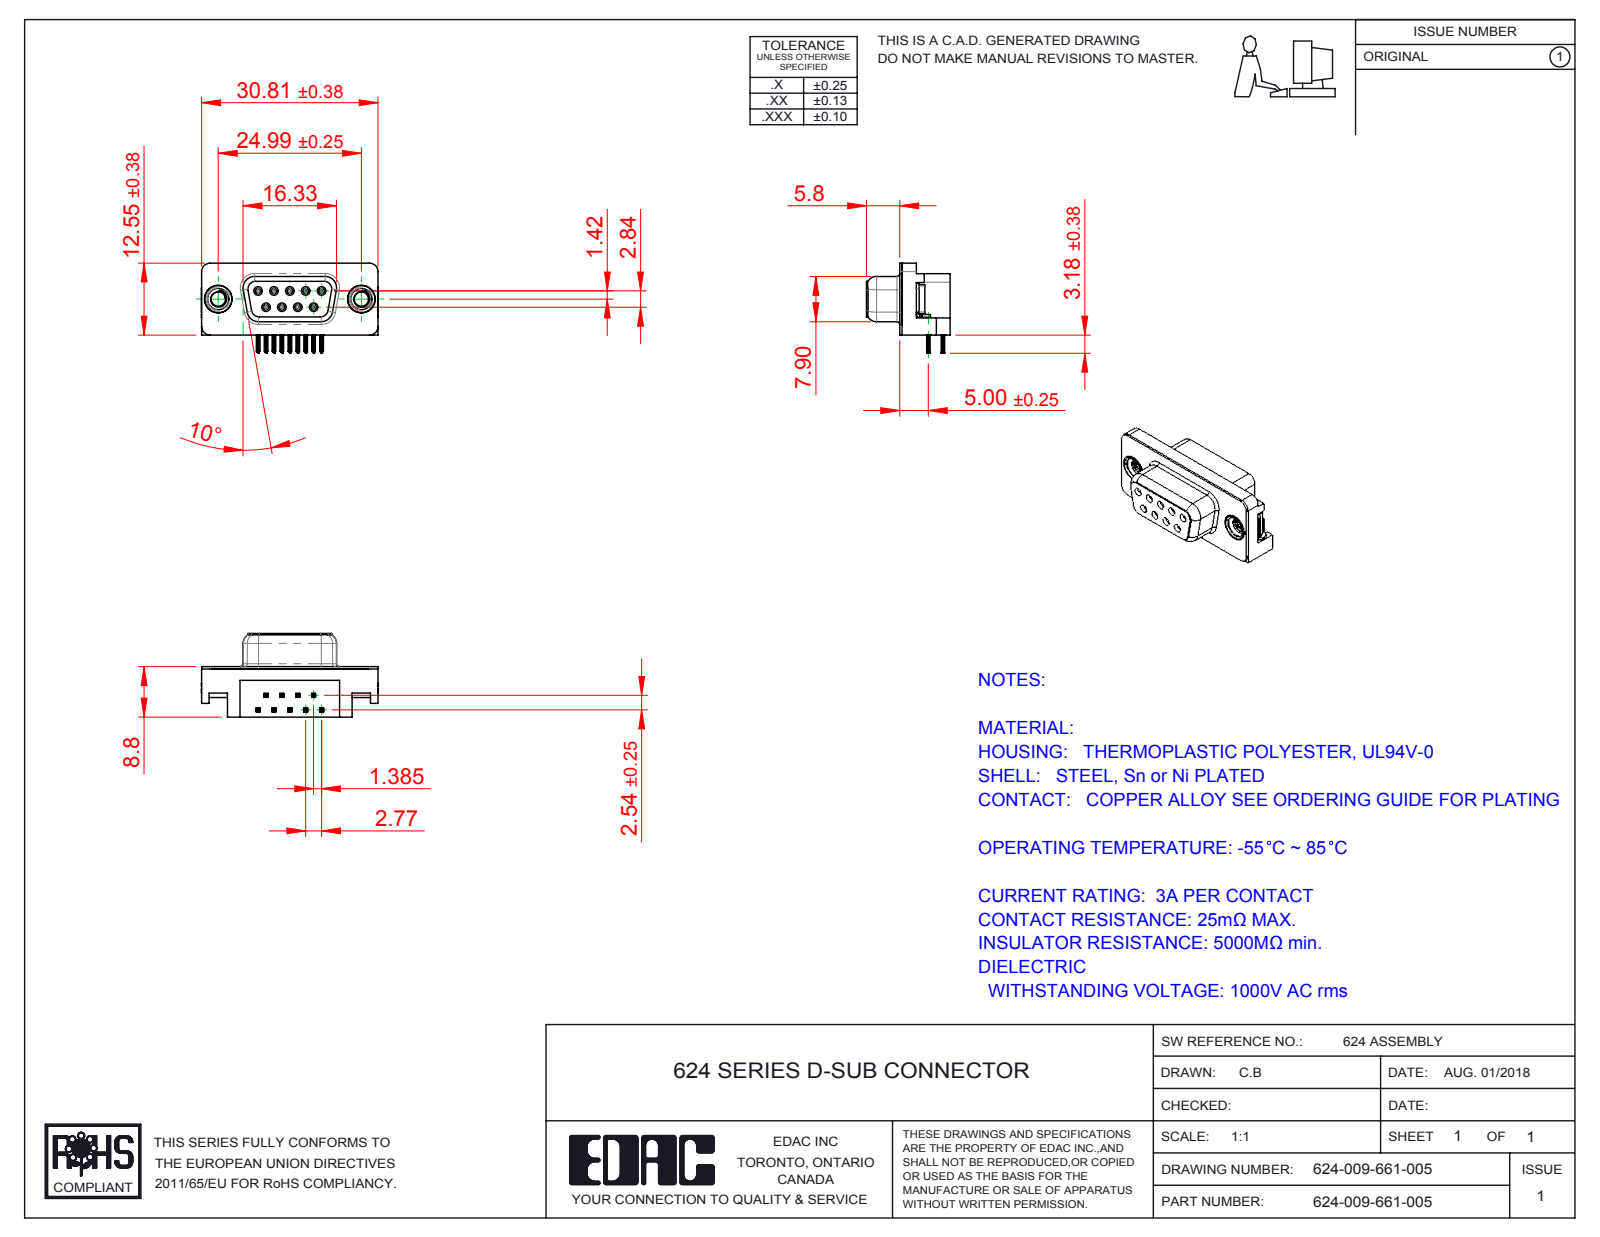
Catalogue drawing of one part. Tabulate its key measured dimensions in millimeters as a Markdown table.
| quantity | value |
| --- | --- |
| part name | 624 Non Board Mount; 624-009-661-005; 624 Shell_9 Socket; 624 Housing_9 Socket (+3 more) |
| STEP written by | SolidWorks 2016 (CONFIG_CONTROL_DESIGN) |
| units | millimeters |
| bodies | 15 solids, 1520 faces (642 planar, 410 cylindrical, 468 other) |
| overall size | 30.89 × 15.73 × 14.6 |
| volume | 2 932 mm³ |
| surface area | 4 338 mm² |
| round holes (diameter × count) | 0.8 × 9, 0.9 × 9, 2.5 × 2, 4 × 2, 4.8 × 2, 5 × 2 |
| round bosses / shafts (diameter × count) | 1.2 × 9, 4.9 × 2, 4.75 × 2, 3.9 × 2 |
| partial cylindrical surfaces (radius × count) | 0.1 × 72, 0.15 × 36, 0.35 × 18, 1 × 18, 0.34 × 9, 0.25 × 8, 1.35 × 8, 1.5 × 7 |
| main face-to-face distances | 0.4, 8.4, 8.8, 2.9, 2.5, 6.2, 5.9, 0.35, 10.69, 10.34 |
| hole center spacings | 3.16, 2.77, 5.54, 5.03, 5.04, 8.31, 7.48, 7.49 |
